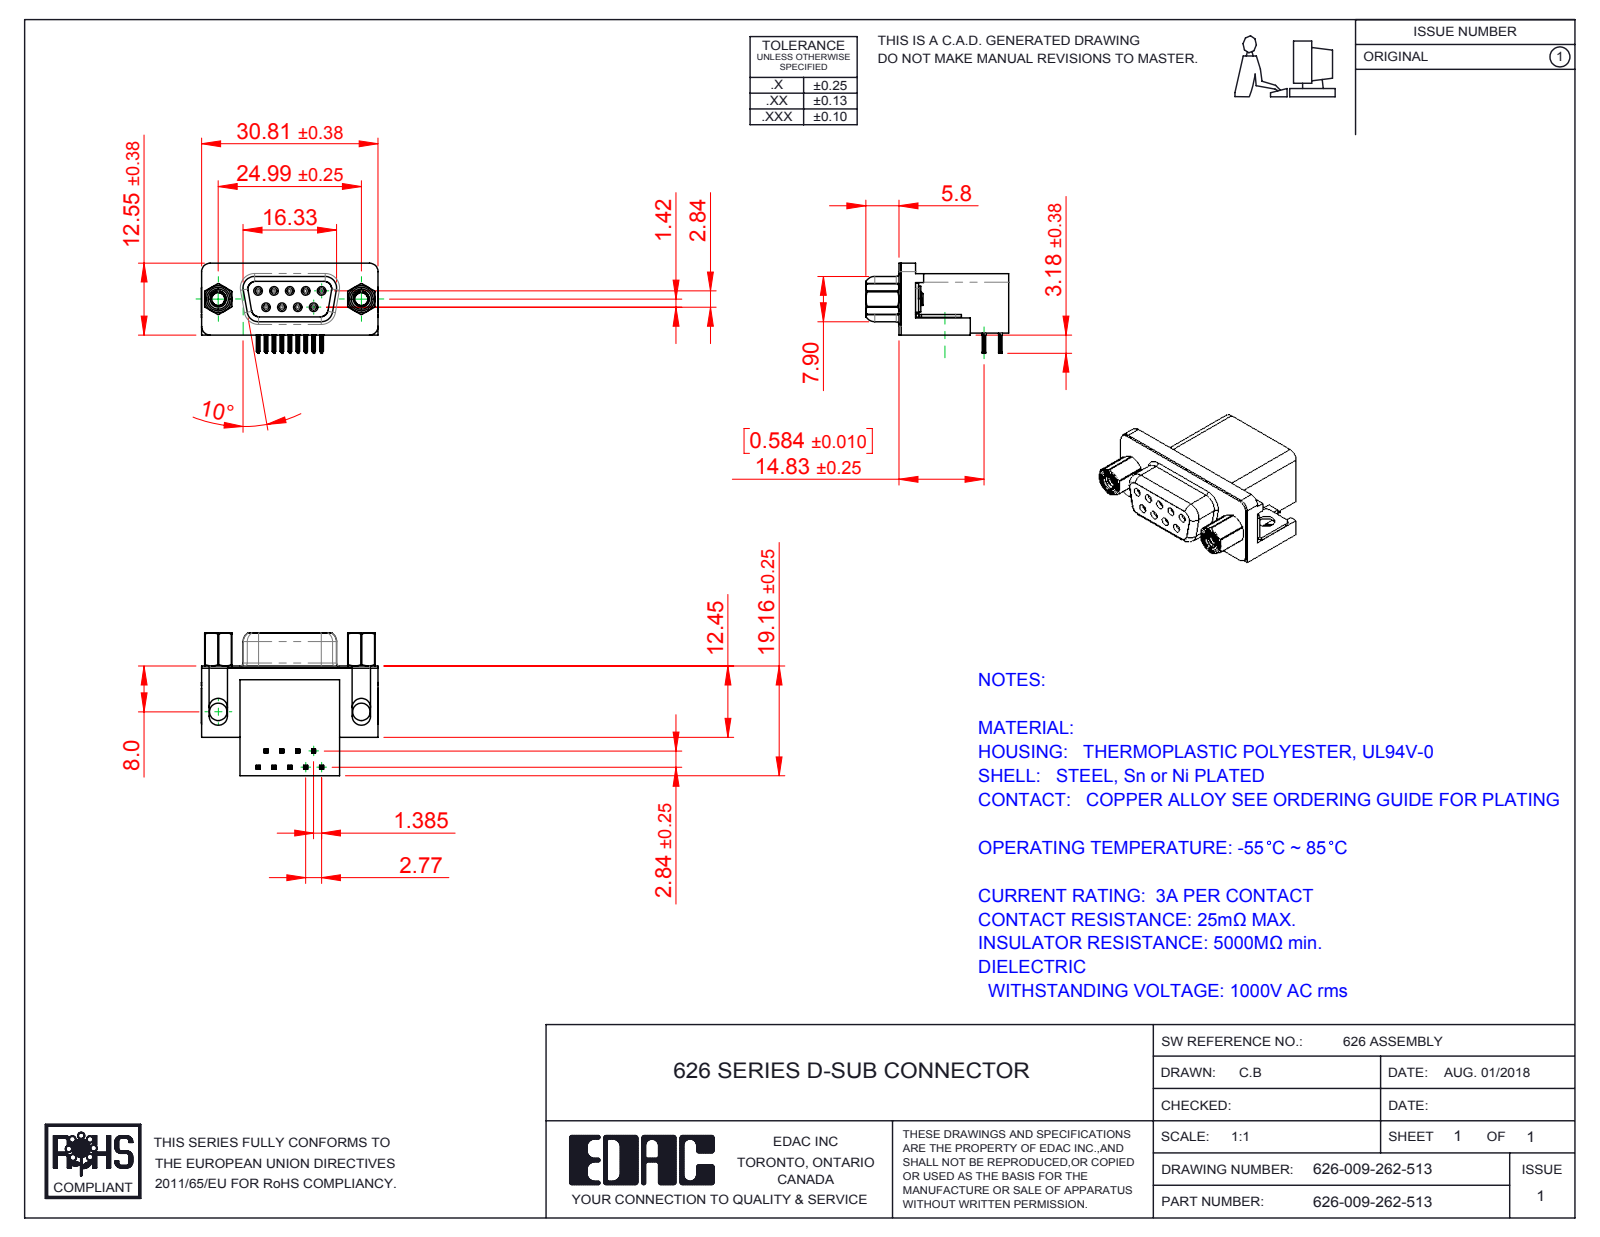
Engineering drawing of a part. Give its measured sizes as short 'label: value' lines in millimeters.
name: 626 Contact Top; 626 Housing_9 Socket; 626-009-262-513; 626 Shell_9 Socket (+4 more)
written by: SolidWorks 2016 (CONFIG_CONTROL_DESIGN)
unit: mm
bodies: 17 solids, 1692 faces (698 planar, 496 cylindrical, 498 other)
size: 30.89 × 24.96 × 15.73
volume: 5 269 mm³; area: 6 460 mm²
holes: 9× ⌀0.8, 9× ⌀0.9, 2× ⌀2.29, 2× ⌀2.3, 2× ⌀3.05, 2× ⌀3.1, 2× ⌀4, 2× ⌀4.8, 2× ⌀5
bosses: 9× ⌀1.2, 2× ⌀4.9, 2× ⌀4.7, 2× ⌀4.5, 2× ⌀3.85, 2× ⌀2.79
rounds: 72× R0.1, 36× R0.15, 18× R0.35, 18× R1, 9× R0.34, 8× R1.35, 8× R1.6, 7× R1.5
face distances: 0.4, 10.34, 0.35, 18.76, 19.16, 16.26, 6.2, 5.8, 2.9, 2.5
hole spacings: 3.16, 2.77, 5.54, 5.03, 5.04, 8.31, 7.48, 7.49
